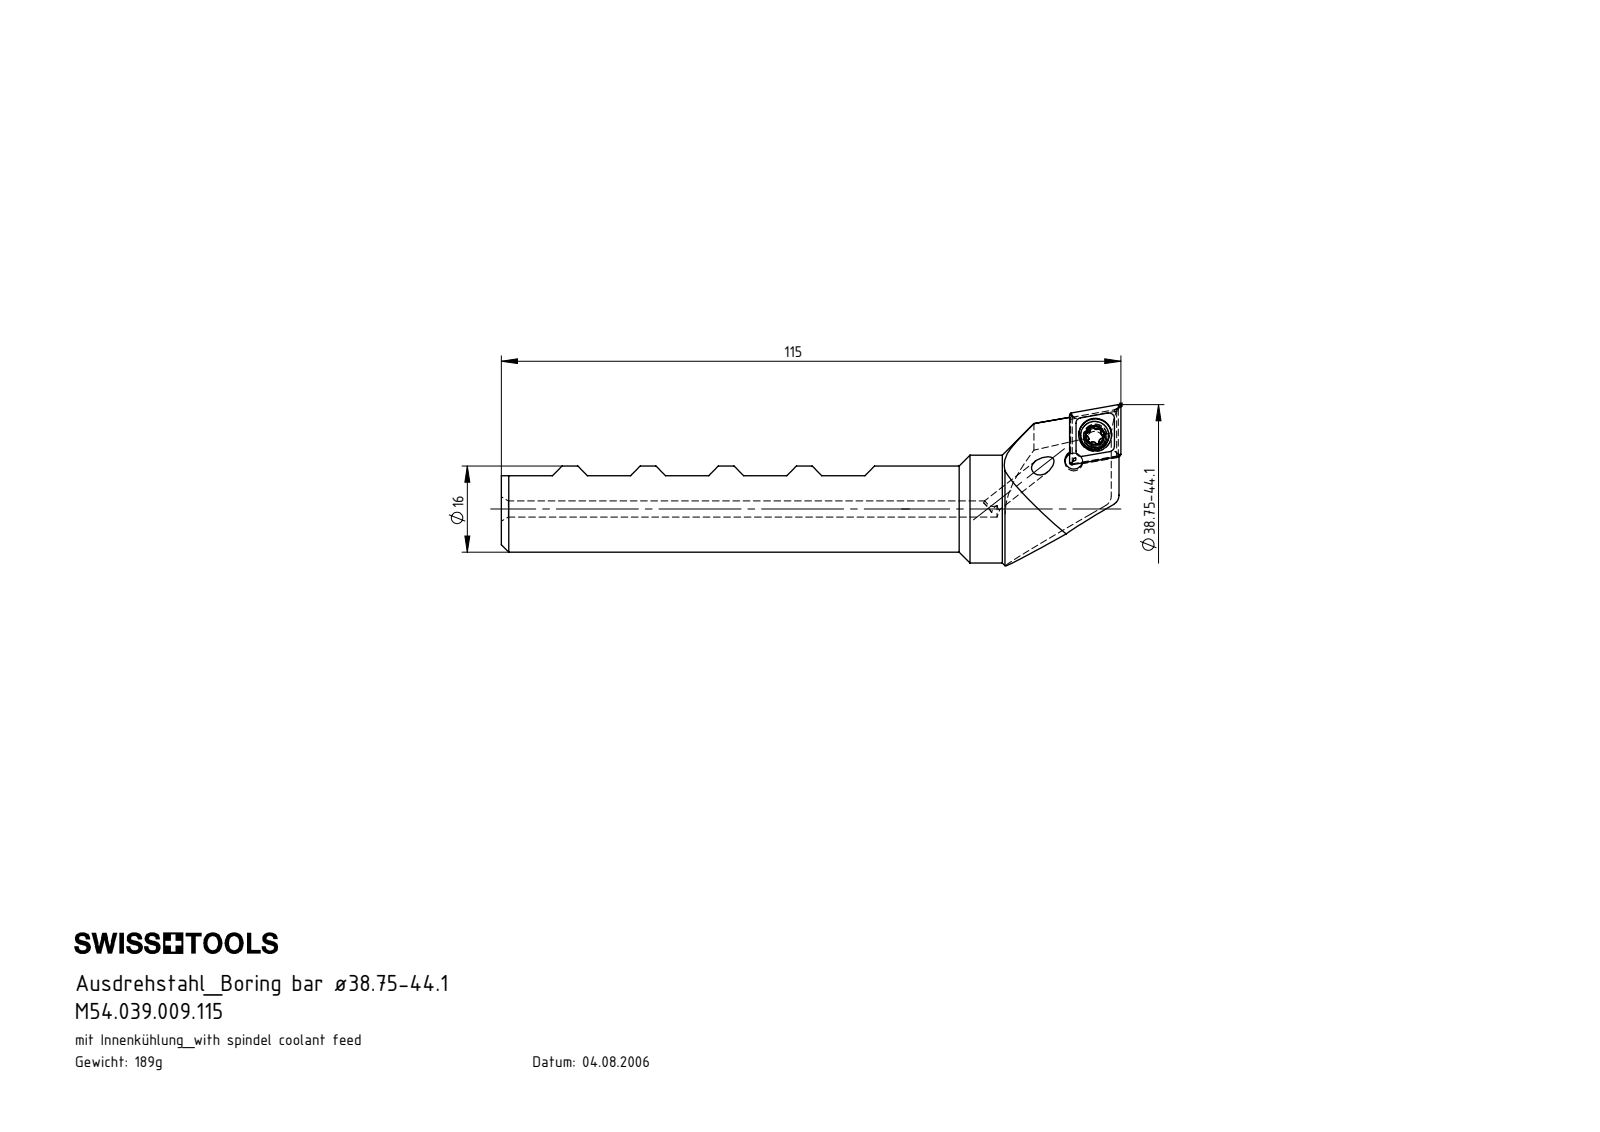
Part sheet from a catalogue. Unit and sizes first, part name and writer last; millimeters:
Units: millimetres
Overall size (bounding box): 115 × 29.88 × 22.27
Round holes (diameter × count): ⌀3 ×2, ⌀3.3 ×2, ⌀4.4 ×1, ⌀6.1 ×1
Round bosses / shafts (diameter × count): ⌀20 ×1, ⌀16 ×1, ⌀5.25 ×1, ⌀4 ×1
Partial cylindrical surfaces — rounded edges, fillets, slot ends (radius × count): R0.34 ×6, R0.59 ×6, R2 ×1, R10.5 ×1, R12 ×1
Main face-to-face distances: 8.22, 10.25, 11.99, 3.77, 20.5, 0.31, 30.76, 20.51, 12.19, 3.97
Hole centre spacings: 6.07, 6.2
Volume: 24 023 mm³ · Surface area: 8 221 mm²
Bodies: 3 solids, 114 faces (45 planar, 25 cylindrical, 44 other)
Part name (STEP PRODUCT): B39-WCB.K11.115_A; WCB-ER2.001.009_A; CCMT09T304; B39.WCB.K11.115
STEP written by: SolidWorks 2017 (AUTOMOTIVE_DESIGN)
